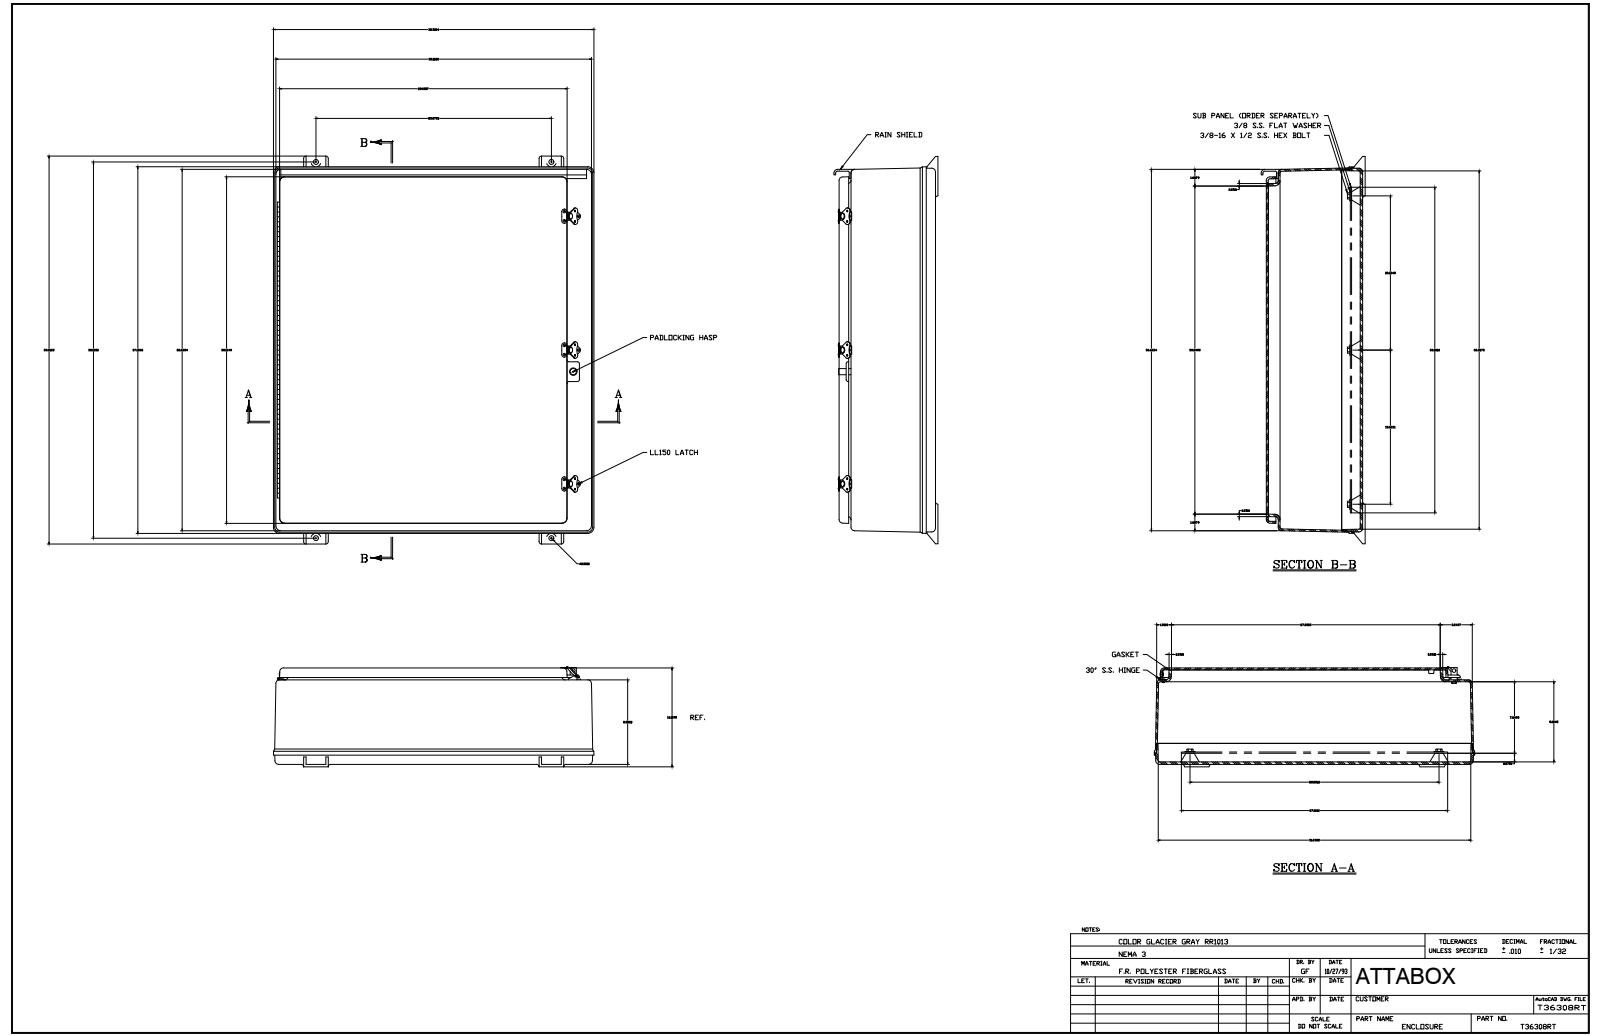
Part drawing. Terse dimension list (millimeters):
name: T36308RT
written by: SolidWorks 2018 (AUTOMOTIVE_DESIGN)
unit: mm
bodies: 49 solids, 1486 faces (581 planar, 594 cylindrical, 311 other)
size: 998.6 × 825.5 × 268.3
volume: 13 750 000 mm³; area: 5 442 000 mm²
holes: 27× ⌀3.3, 12× ⌀1.6, 8× ⌀1.7, 6× ⌀3.5, 6× ⌀4.7, 4× ⌀14.3, 3× ⌀1.7, 2× ⌀11, 2× ⌀13, 2× ⌀13, 1× ⌀3.2, 1× ⌀3.4
bosses: 12× ⌀3.6, 11× ⌀7.5, 3× ⌀12.7, 1× ⌀6.4, 1× ⌀5.1, 1× ⌀5.1, 1× ⌀3.4
rounds: 86× R0.3, 24× R4.8, 24× R6.4, 17× R9.5, 13× R8, 12× R0.8, 12× R12.7, 7× R2.5
face distances: 6.4, 4.8, 248.4, 242.1, 243.7, 237.3, 4.7, 4.8, 217.5, 212.7
hole spacings: 344.5, 241.3, 495.3, 689, 88.2, 345, 396.9, 483.7
